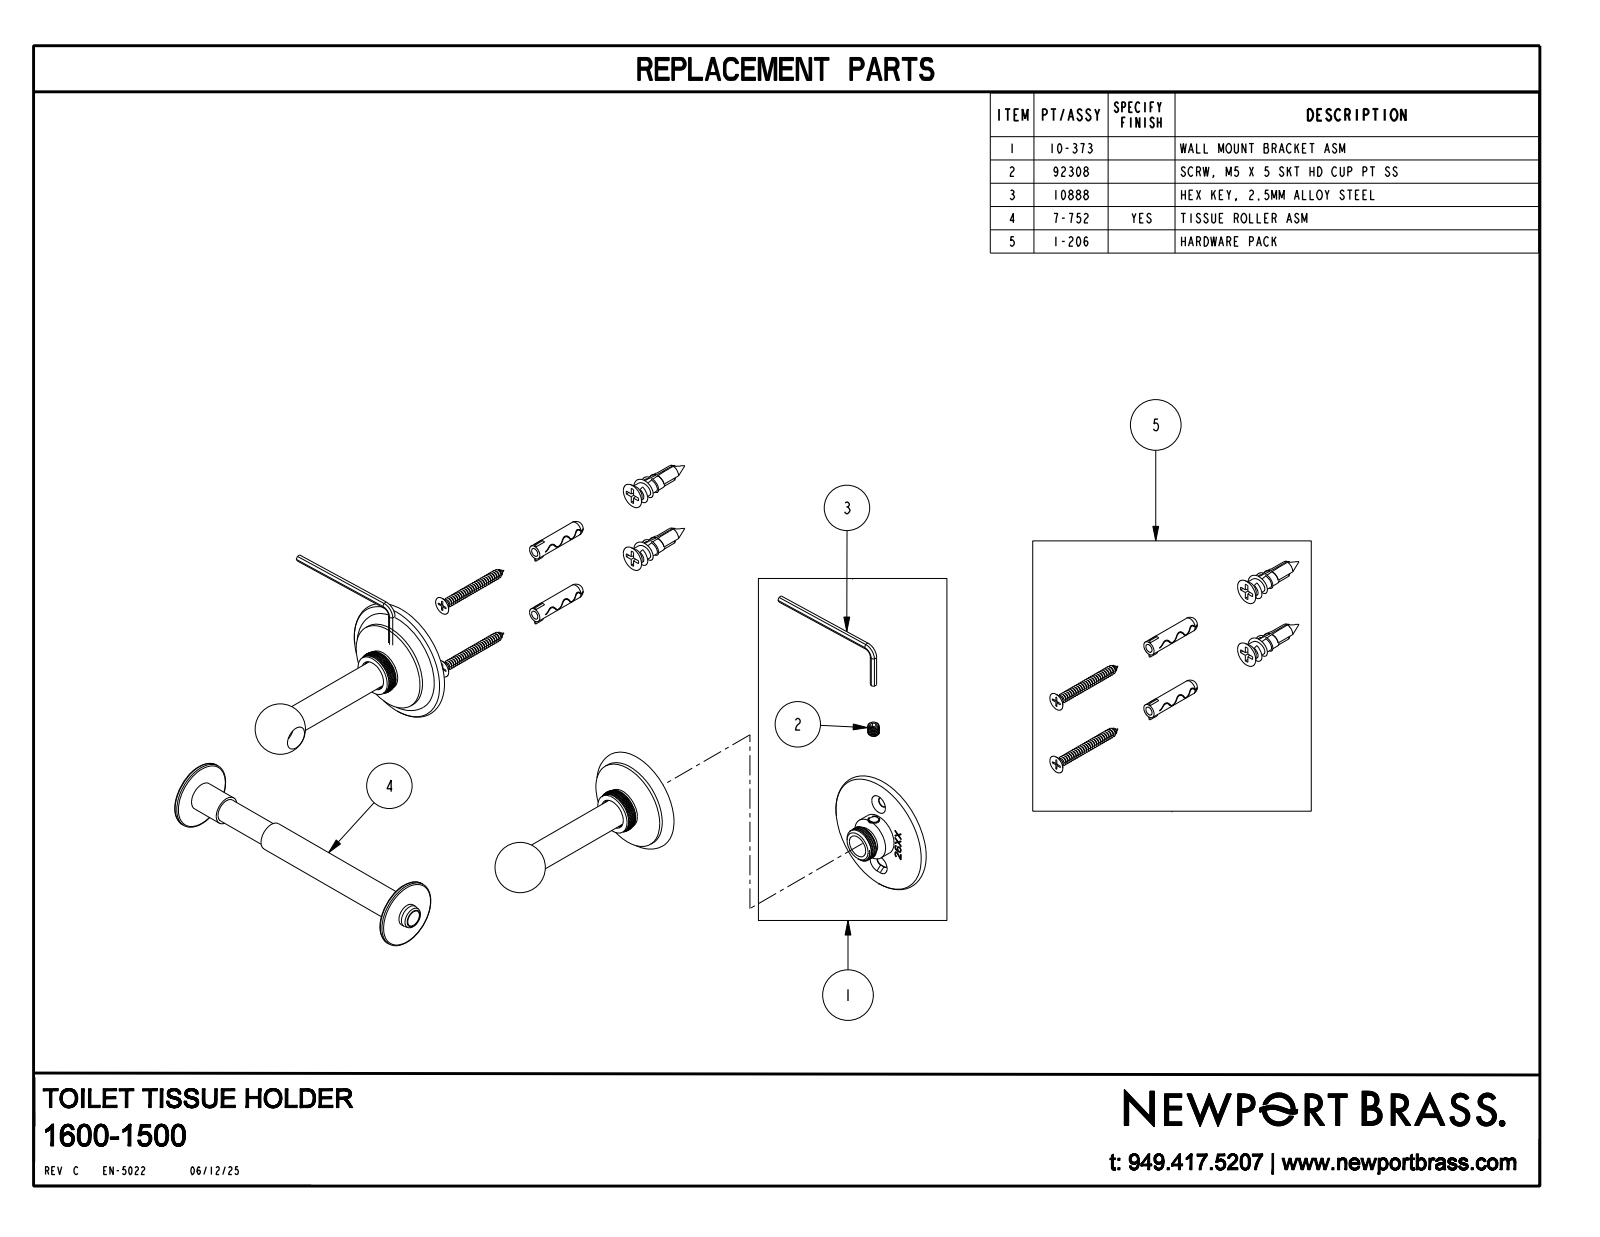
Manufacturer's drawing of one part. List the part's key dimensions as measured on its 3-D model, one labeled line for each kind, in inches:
Part name (STEP PRODUCT): 40805; 26XX; 40806; 92308 (+7 more)
STEP written by: CREO PARAMETRIC BY PTC INC, 2018400 (CONFIG_CONTROL_DESIGN)
Units: inches
Bodies: 13 solids, 1332 faces (643 planar, 283 cylindrical, 406 other)
Overall size (bounding box): 7.953 × 3.543 × 2.126
Volume: 3.514 in³ · Surface area: 97.89 in²
Round holes (diameter × count): ⌀0.157 ×2, ⌀0.165 ×2, ⌀0.177 ×2, ⌀0.197 ×2, ⌀0.394 ×2, ⌀0.496 ×2, ⌀0.555 ×2, ⌀0.62 ×2, ⌀1.583 ×2, ⌀1.89 ×2, ⌀0.13 ×1, ⌀0.157 ×1
Round bosses / shafts (diameter × count): ⌀1.551 ×2, ⌀0.748 ×2, ⌀0.709 ×2, ⌀0.59 ×2, ⌀0.503 ×2, ⌀0.472 ×2, ⌀0.374 ×2, ⌀0.264 ×2
Partial cylindrical surfaces — rounded edges, fillets, slot ends (radius × count): R0.089 ×4
Main face-to-face distances: 0.098, 0.079, 4.987, 0.118, 0.02, 4.908, 5.066, 0.709, 0.689, 0.591
Hole centre spacings: 5.827, 0.625, 5.861
